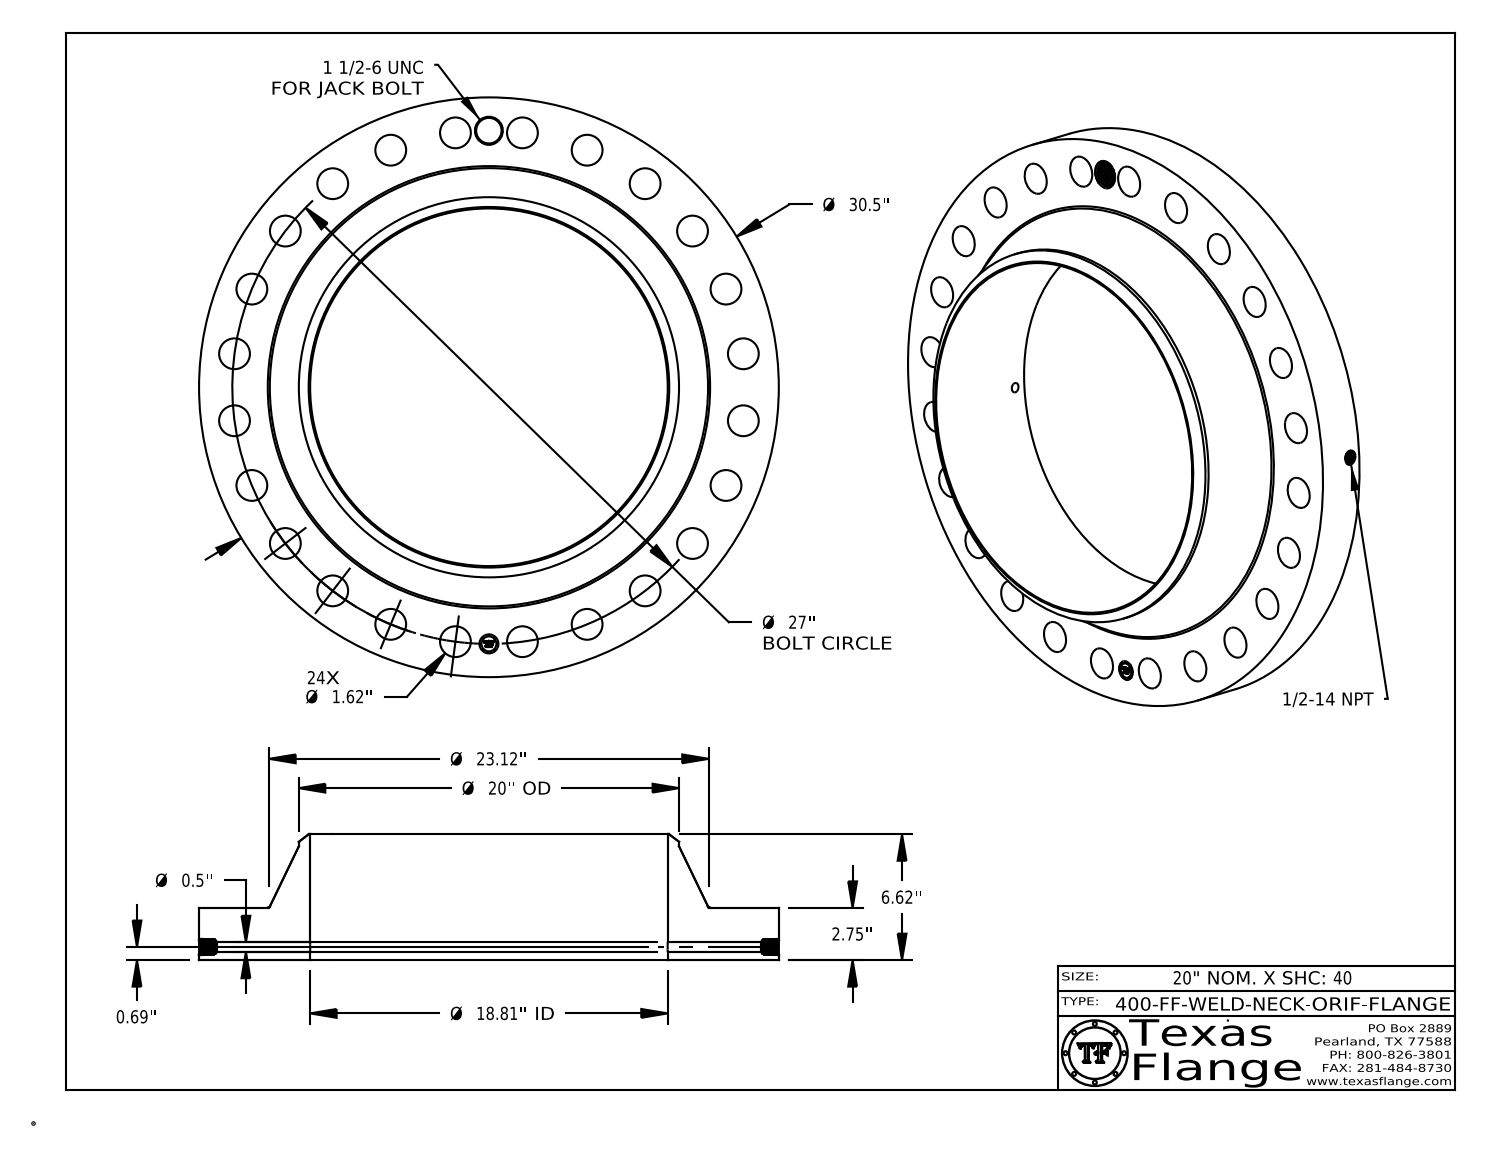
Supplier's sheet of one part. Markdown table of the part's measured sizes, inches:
| quantity | value |
| --- | --- |
| part name | 400-FF-WELD-NECK |
| STEP written by | CATIA V5 STEP AP214 (AUTOMOTIVE_DESIGN) |
| units | inches |
| bodies | 1 solid, 807 faces (368 planar, 127 cylindrical, 312 other) |
| overall size | 30.5 × 30.5 × 6.62 |
| volume | 1 403 in³ |
| surface area | 1 992 in² |
| round holes (diameter × count) | 1.62 × 24, 0.5 × 1, 0.672 × 1, 1 × 1, 1.344 × 1, 18.812 × 1 |
| round bosses / shafts (diameter × count) | 0.061 × 8, 30.5 × 1, 20 × 1, 0.788 × 1 |
| main face-to-face distances | 2.75, 6.62, 3.87, 2.735, 0.015, 3.885, 0.298, 0.293, 0.054, 0.248 |
| hole center spacings | 13.5, 23.383, 24.945, 21.42, 3.524, 6.988, 19.092, 26.08 |
